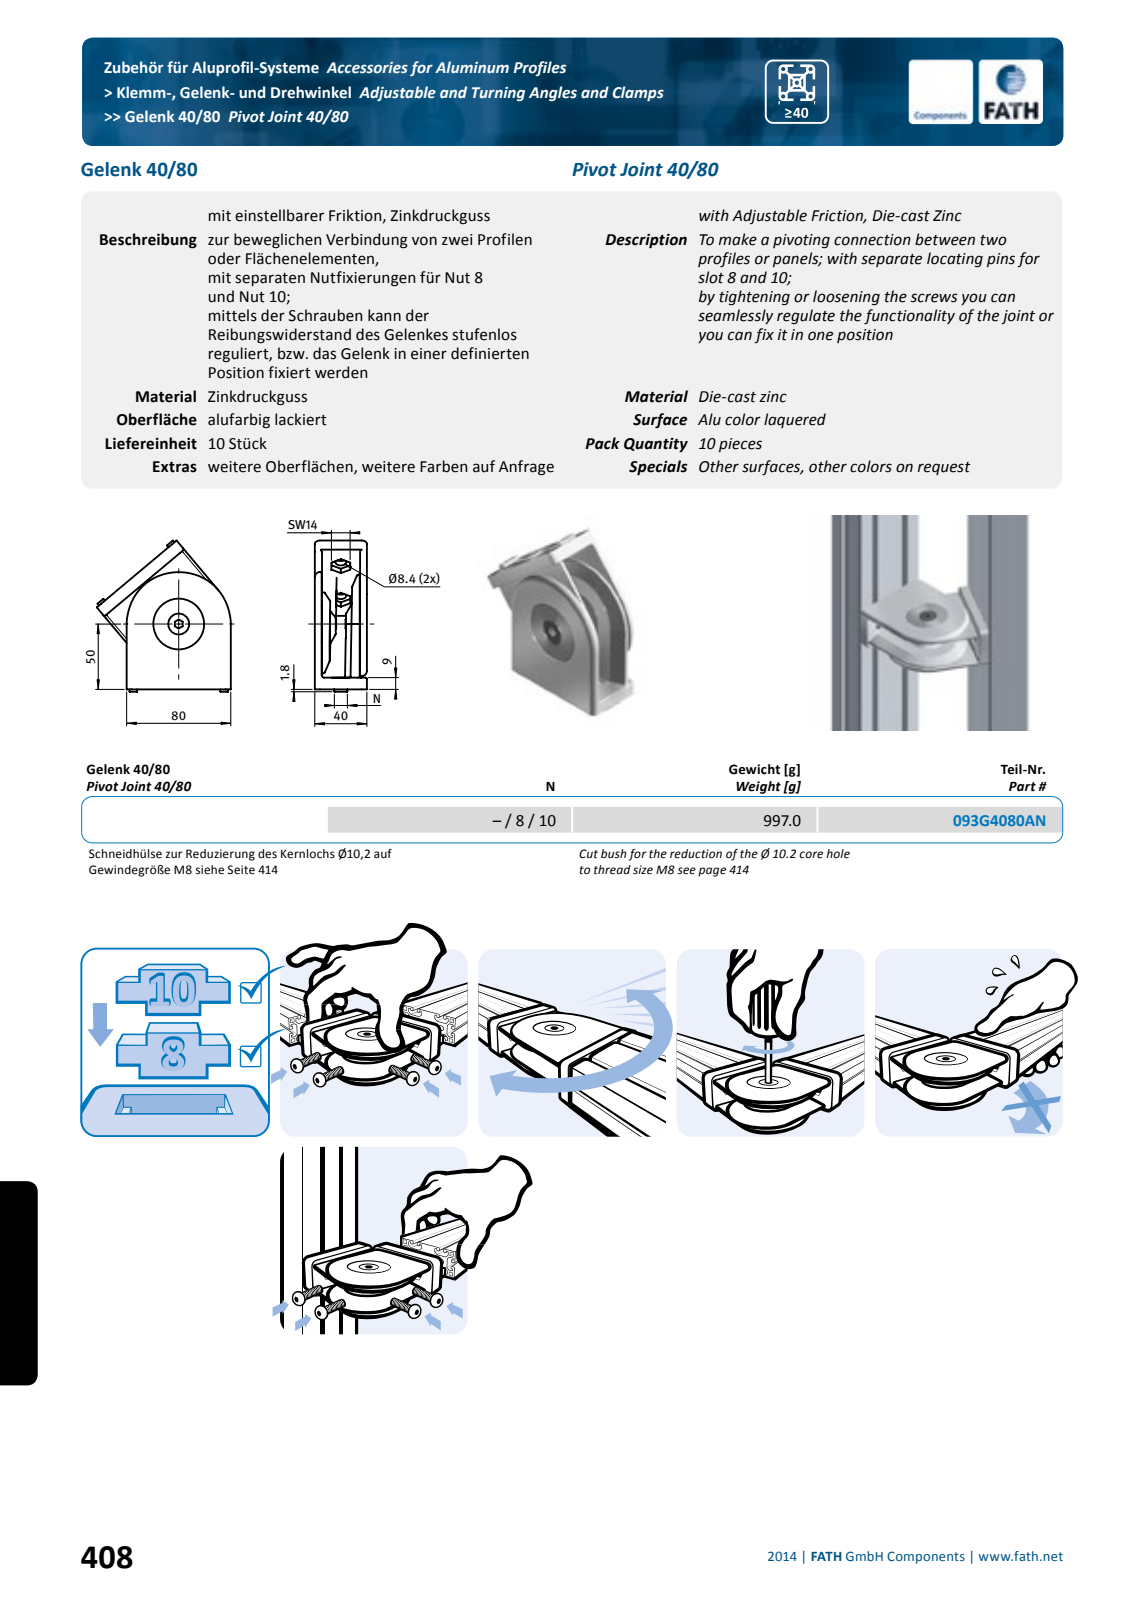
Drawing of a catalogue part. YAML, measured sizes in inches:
part_name: "fath_093g4080an_1; fath_093g4080an_2; fath_093g4080an_3; fath_093g4080an_4 (+8 more)"
step_written_by: "Spatial InterOp 3D (automotive_design)"
units: inches
bodies: {solids: 13, faces: 1432, planar: 323, cylindrical: 413, other: 696}
overall_size: [4.558, 4.033, 3.177]
volume: 11.32
surface_area: 135.2
round_holes:
  - {diameter: 0.268, count: 1}
  - {diameter: 0.323, count: 1}
  - {diameter: 0.327, count: 1}
  - {diameter: 0.354, count: 1}
  - {diameter: 0.551, count: 1}
  - {diameter: 0.787, count: 1}
  - {diameter: 2.378, count: 1}
  - {diameter: 2.756, count: 1}
round_bosses_or_shafts:
  - {diameter: 0.079, count: 4}
  - {diameter: 3.134, count: 1}
  - {diameter: 2.976, count: 1}
  - {diameter: 2.74, count: 1}
  - {diameter: 2.362, count: 1}
  - {diameter: 1.575, count: 1}
  - {diameter: 1.102, count: 1}
  - {diameter: 0.63, count: 1}
partial_cylinders:
  - {radius: 0.008, count: 134}
  - {radius: 0.039, count: 44}
  - {radius: 0.079, count: 39}
  - {radius: 0.02, count: 24}
  - {radius: 0.157, count: 8}
  - {radius: 0.016, count: 6}
  - {radius: 0.012, count: 4}
  - {radius: 0.059, count: 4}
face_to_face_distances: [0.205, 1.362, 1.567, 1.157, 1.35, 0.217, 1.146, 1.358, 1.134, 0.039]
